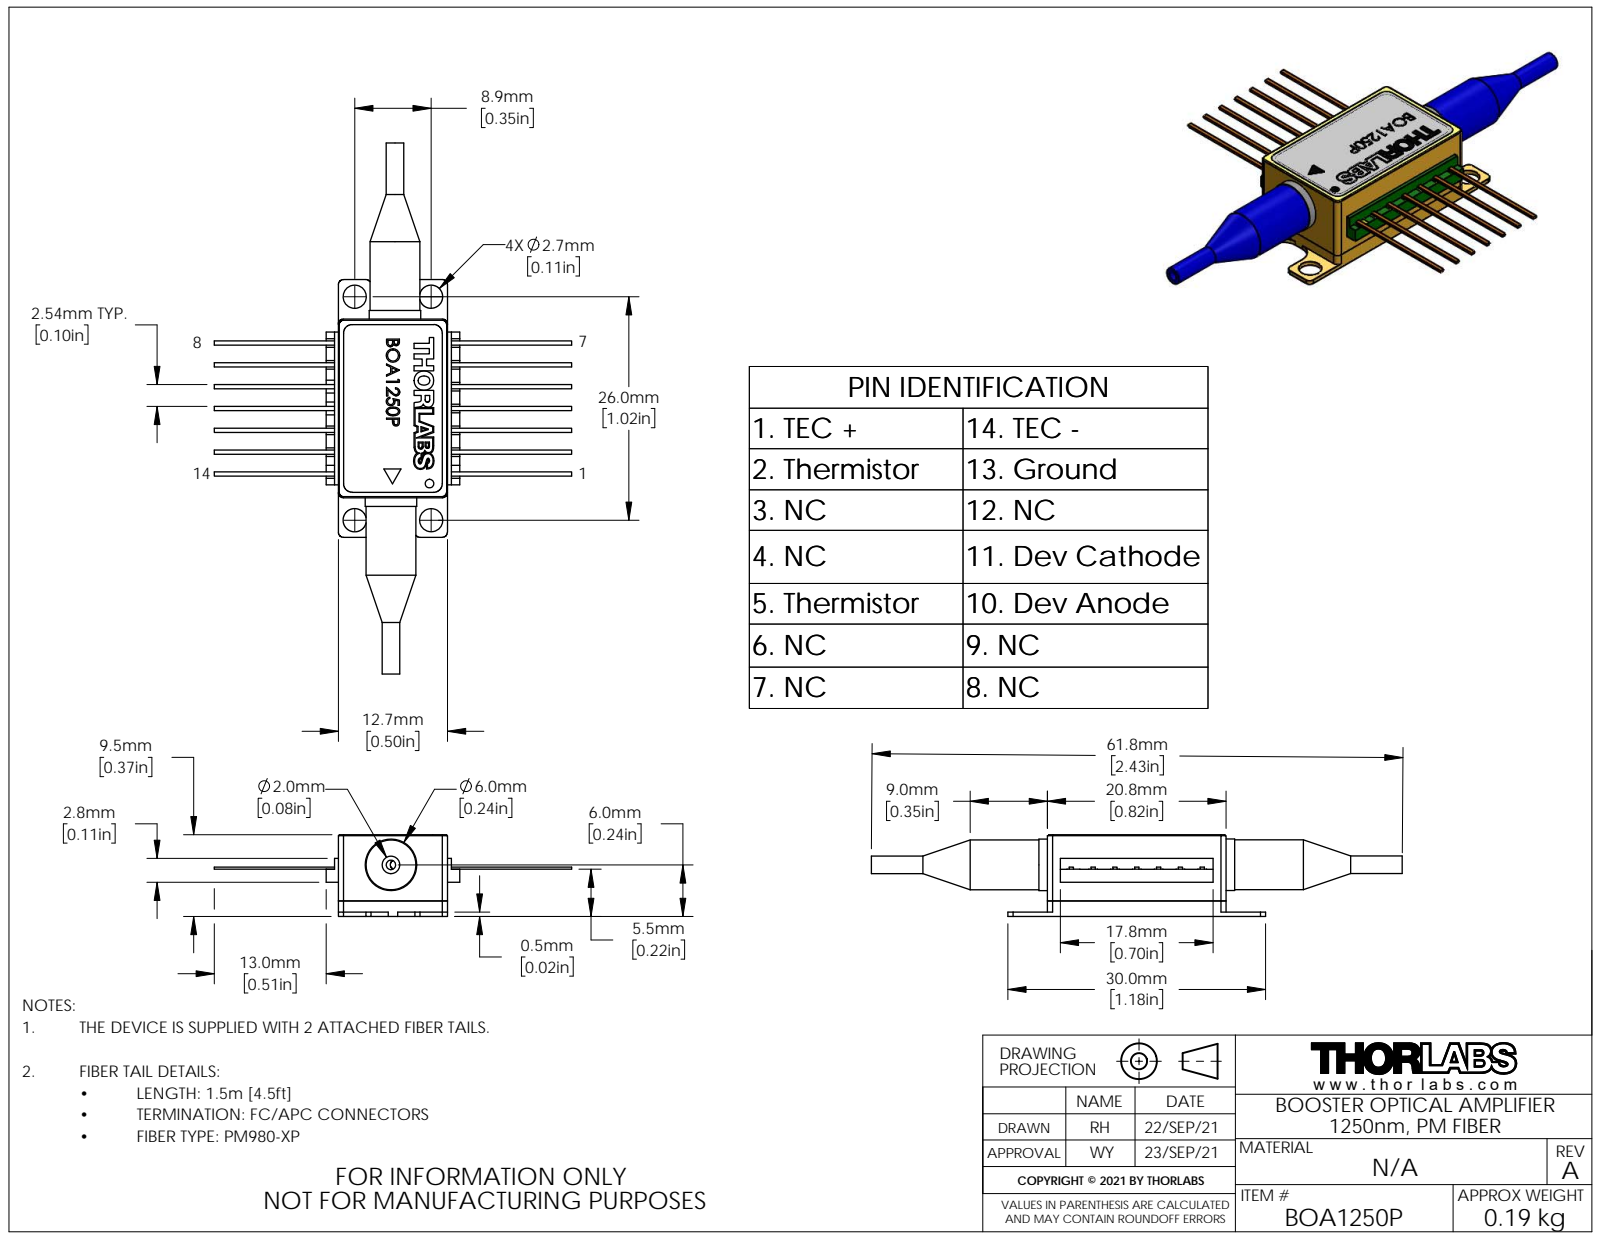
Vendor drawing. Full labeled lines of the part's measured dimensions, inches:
Part name (STEP PRODUCT): QTN042710-E0W
STEP written by: SolidWorks 2018 (AUTOMOTIVE_DESIGN)
Units: inches
Bodies: 0 solids, 390 faces (267 planar, 50 cylindrical, 73 other)
Overall size (bounding box): 2.433 × 1.638 × 0.374
Round holes (diameter × count): ⌀0.106 ×4, ⌀0.043 ×2, ⌀0.039 ×1
Round bosses / shafts (diameter × count): ⌀0.236 ×2, ⌀0.228 ×2, ⌀0.08 ×2
Partial cylindrical surfaces — rounded edges, fillets, slot ends (radius × count): R0.024 ×12, R0.02 ×4, R0.079 ×4
Main face-to-face distances: 0.374, 0.5, 0.156, 0.218, 0.217, 0.06, 0.157, 0.02, 0.07, 0.226
Hole centre spacings: 0.35, 1.024, 1.082, 0.018, 0.168, 0.381, 0.856, 0.922
